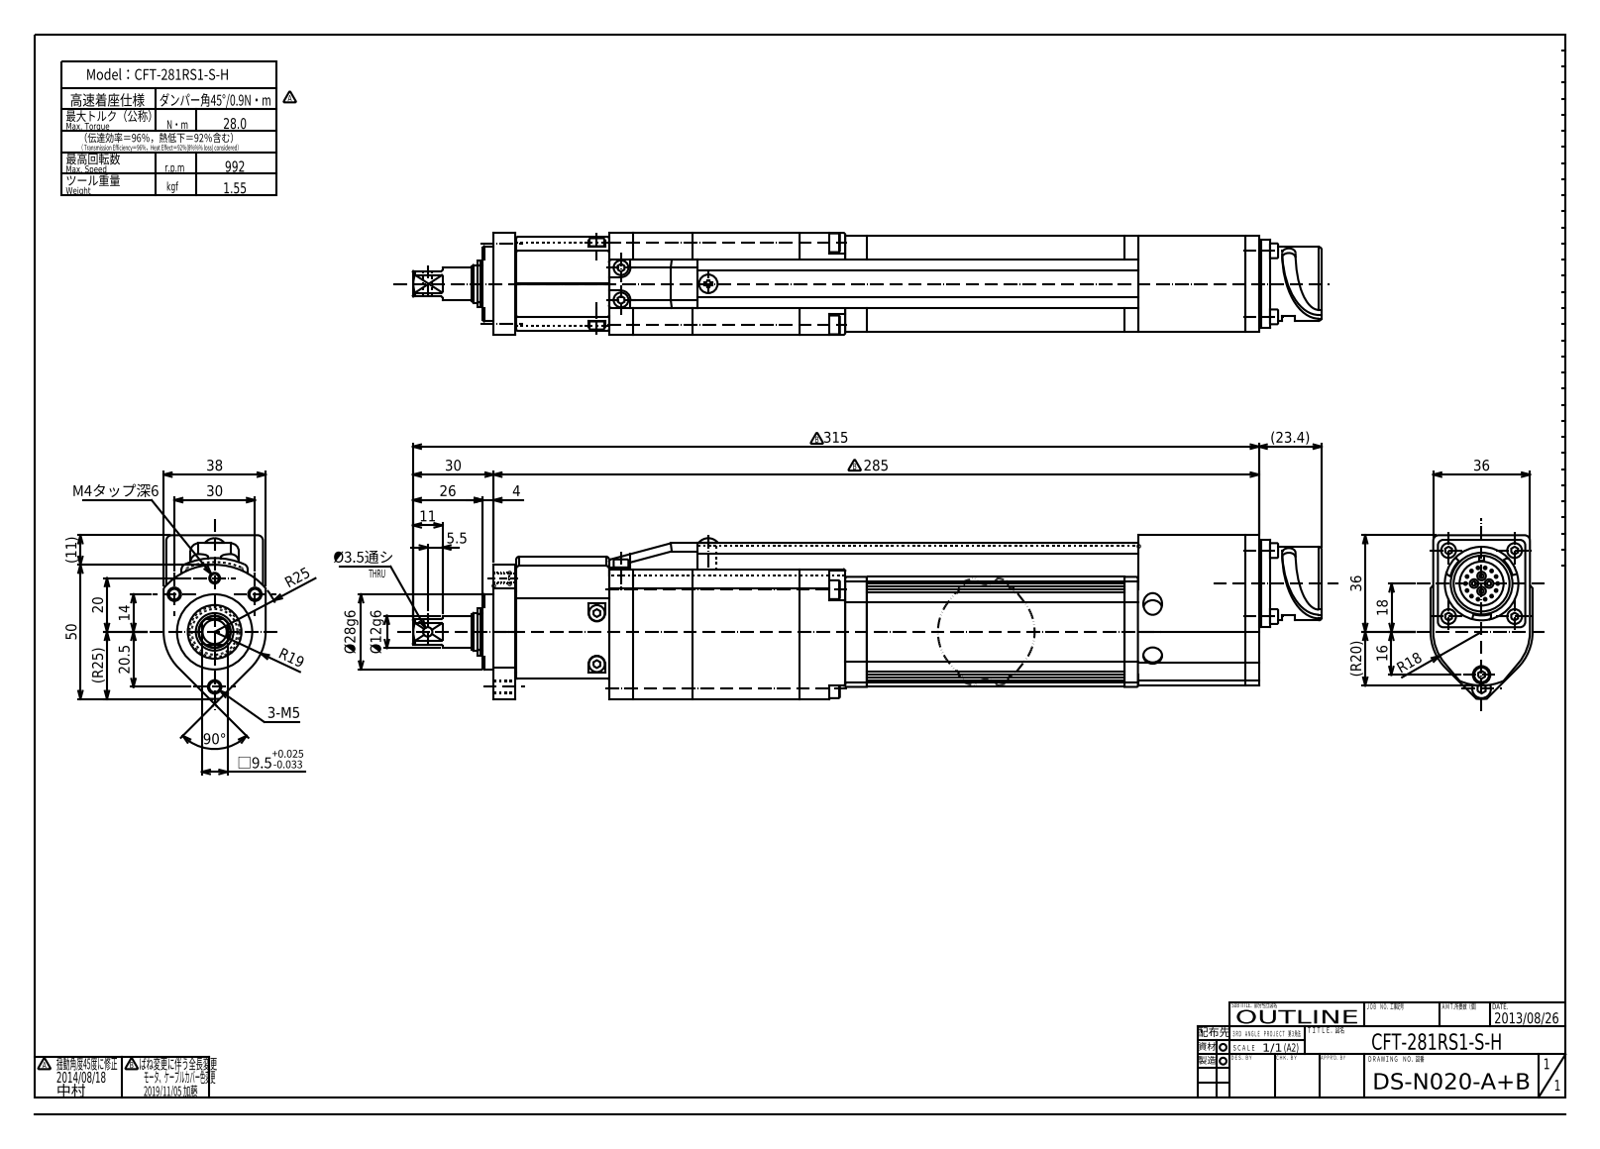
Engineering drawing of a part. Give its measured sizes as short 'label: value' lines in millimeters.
name: CFT-281RS1-S-H(DS-N020+F)_OUTLINE_20201118
written by: Autodesk Inventor 2021 (AUTOMOTIVE_DESIGN)
unit: mm
bodies: 1 solid, 700 faces (436 planar, 188 cylindrical, 76 other)
size: 338.4 × 61 × 38
volume: 438 498 mm³; area: 59 895 mm²
holes: 4× ⌀3.24, 3× ⌀4.13, 2× ⌀1.2, 2× ⌀7, 1× ⌀3.5, 1× ⌀6.5, 1× ⌀14.7, 1× ⌀20.8
bosses: 14× ⌀1, 11× ⌀5.5, 4× ⌀1.6, 3× ⌀7, 2× ⌀6, 2× ⌀4.5, 1× ⌀30, 1× ⌀28
rounds: 7× R3, 6× R0.3, 6× R2, 6× R2.75, 5× R4, 4× R0.5, 4× R3.25, 3× R1
face distances: 1, 10, 27, 9, 28, 37, 36, 3, 0.5, 18
hole spacings: 16.16, 0.85, 7.76, 10.7, 12.67, 14.53, 15.17, 15.52
